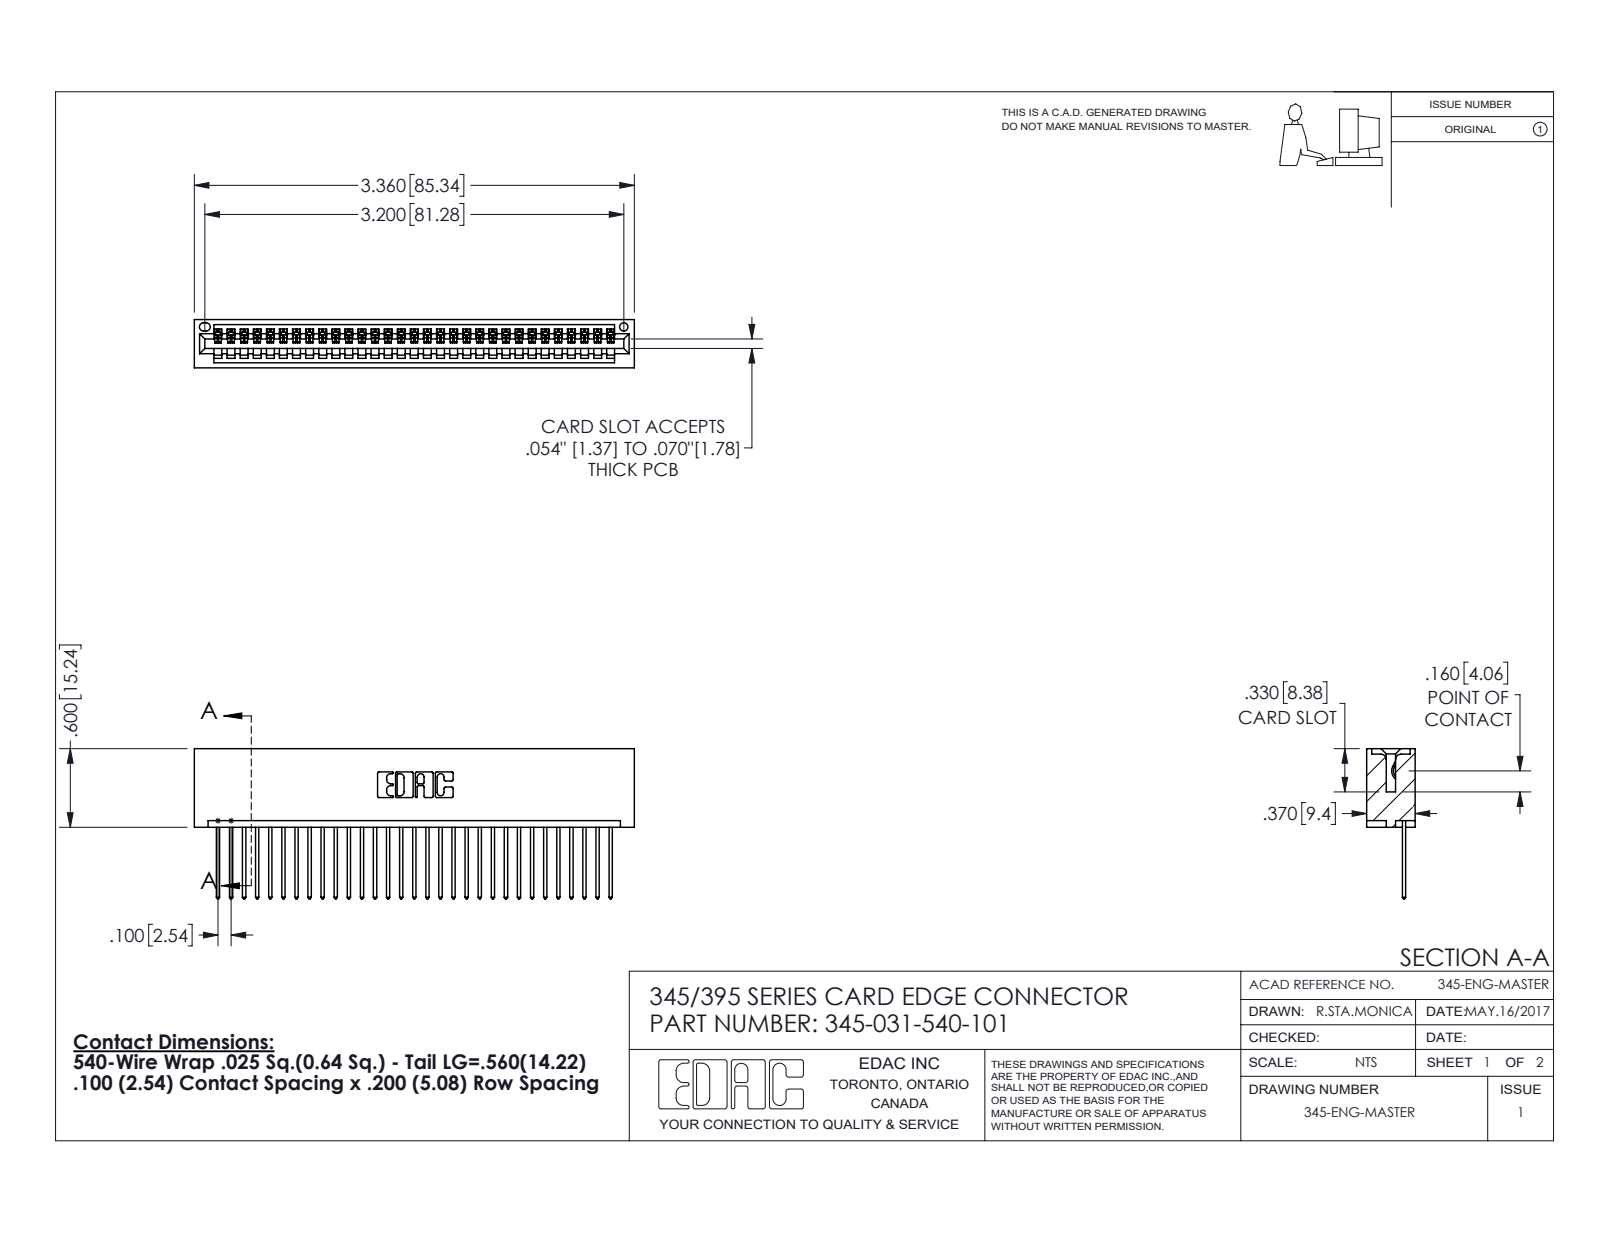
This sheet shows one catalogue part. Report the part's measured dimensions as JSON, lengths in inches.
{"part_name": "345-292-001_345-293-140; 345-031-540-101; 345 Part_No Mounting Lugs", "step_written_by": "SolidWorks 2016 (CONFIG_CONTROL_DESIGN)", "units": "inches", "bodies": {"solids": 32, "faces": 1916, "planar": 1316, "cylindrical": 600, "other": 0}, "overall_size": [3.36, 1.147, 0.37], "volume_in3": 0.527, "surface_area_in2": 18.33, "round_holes": [[0.064, 1]], "partial_cylinders_radius": [[0.006, 62], [0.01, 62], [0.01, 22], [0.007, 6], [0.031, 6], [0.026, 3], [0.031, 2], [0.04, 2]], "face_to_face_distances": [0.072, 0.298, 0.2, 0.37, 0.098, 0.272, 0.025, 0.225, 0.149, 0.072]}
